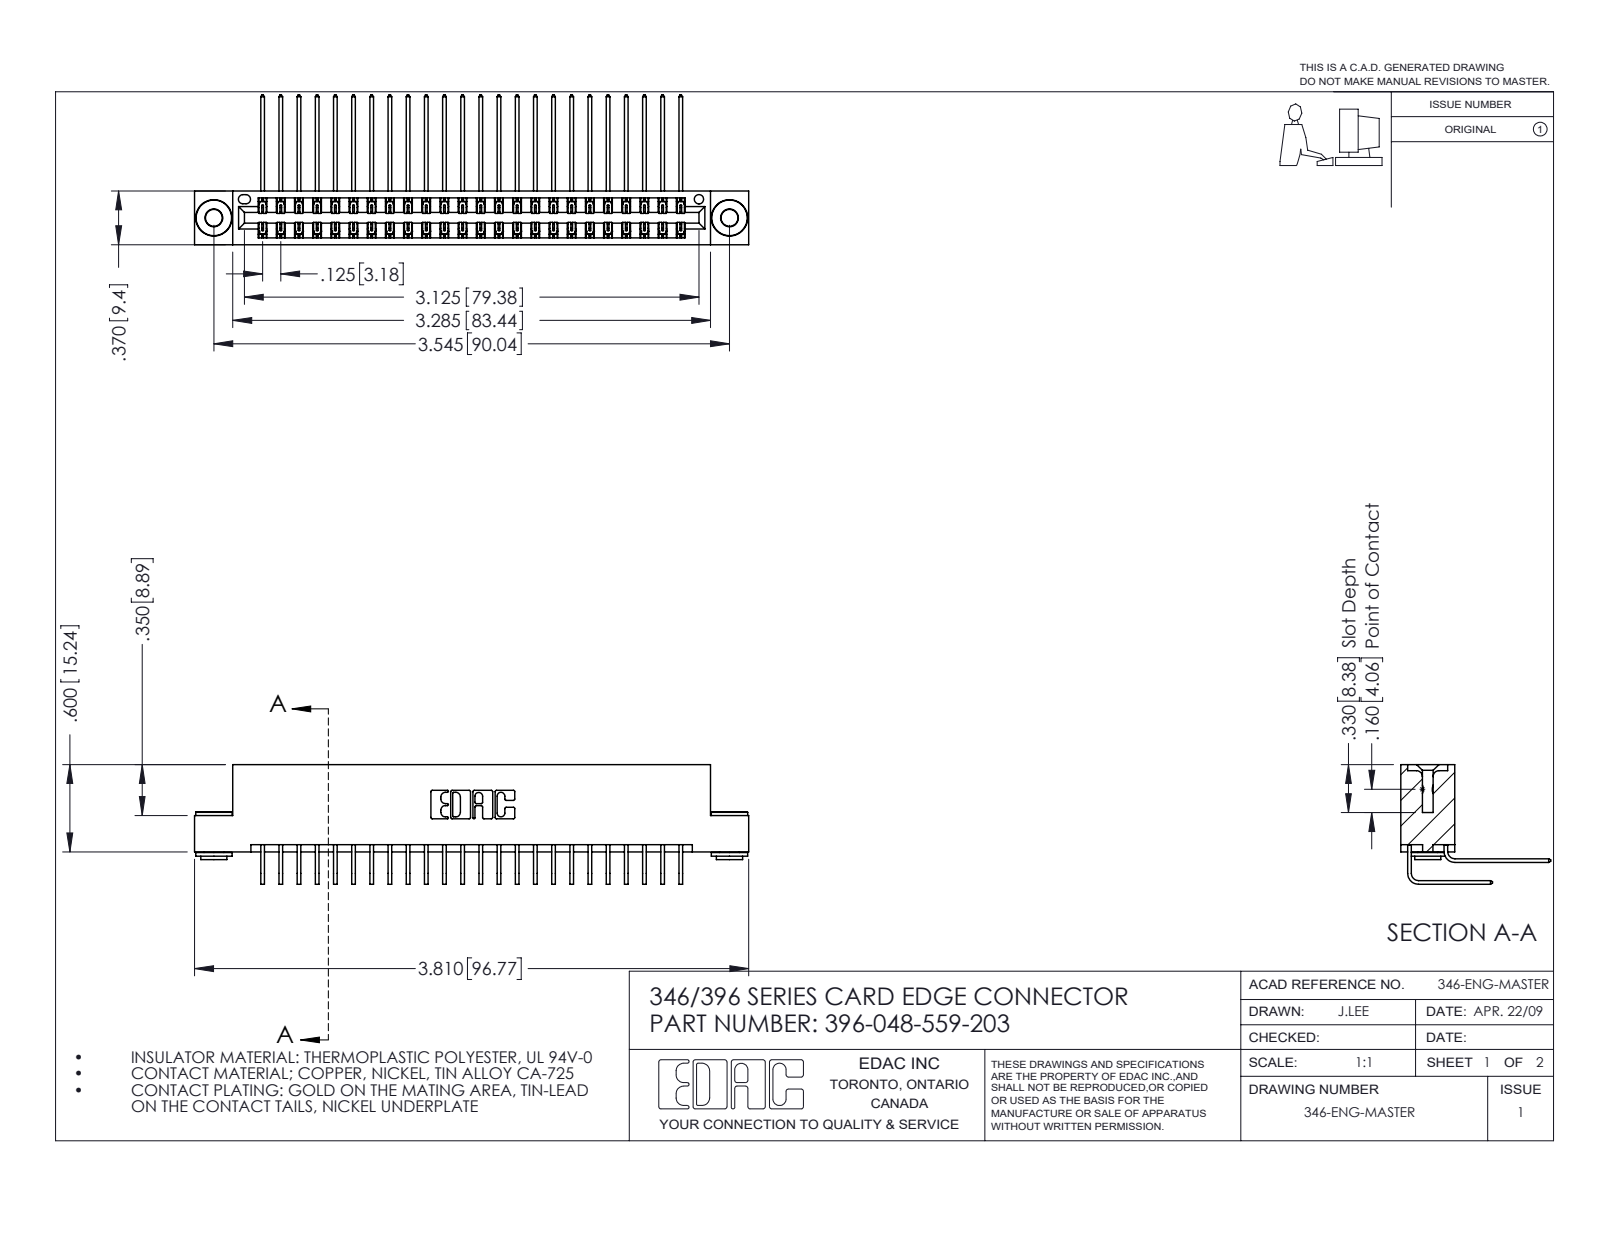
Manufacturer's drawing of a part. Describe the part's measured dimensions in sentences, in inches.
The part is named "345-292-001_559 Tail - 2; 346 Part_Flush Mounting Lugs - 0.156 Dia-TH; 345-250-002_345-250-002-102; 396-048-559-203 (+1 more)". Its 3-D file was written by "SolidWorks 2016 (CONFIG_CONTROL_DESIGN)". It is 51 solids with 2752 faces: 1862 planar, 882 cylindrical and 8 other. Overall it measures 3.81 by 1.03 by 0.823 inches. Its volume is 0.585 cubic inches and its surface area 22.39 square inches. Round holes: 2 of diameter 0.116, 2 of diameter 0.156, 1 of diameter 0.064. Round bosses or shafts: 2 of diameter 0.25, 2 of diameter 0.18, 2 of diameter 0.136. Partial cylindrical surfaces (rounded edges, fillets, slot ends): 72 of radius 0.006, 22 of radius 0.01, 6 of radius 0.007, 6 of radius 0.031, 3 of radius 0.026, 2 of radius 0.014, 2 of radius 0.022, 2 of radius 0.024. The main face-to-face distances are 0.048, 0.322, 0.25, 0.025, 0.37, 0.072, 0.298, 0.275, 0.148, 0.222. The hole center spacings are 0.246, 3.337, 3.545.
